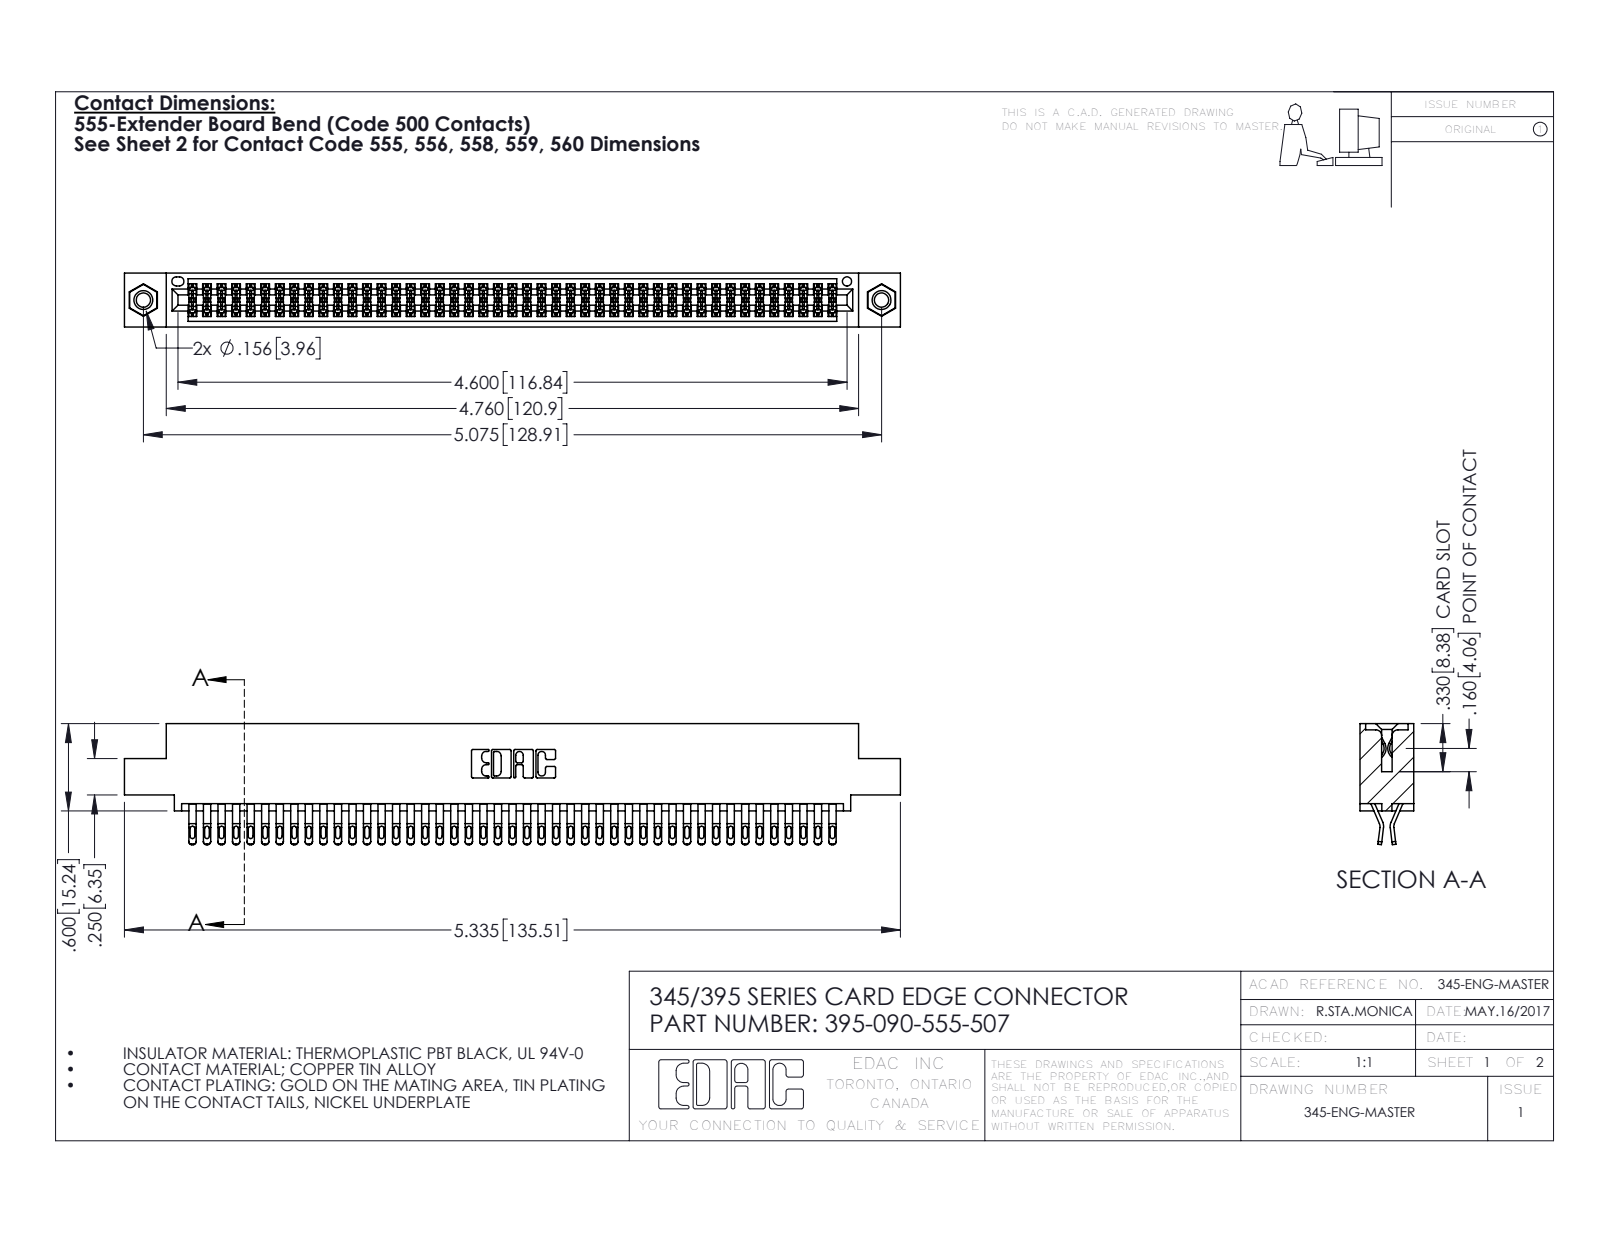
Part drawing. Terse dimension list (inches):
name: 345-292-001_555 Tail; 345 Part_0.110 Offset - 0.156 Dia-TI; 345-250-001_345-250-005-103; 395-090-555-507
written by: SolidWorks 2016 (CONFIG_CONTROL_DESIGN)
unit: in
bodies: 93 solids, 5230 faces (2906 planar, 2308 cylindrical, 16 other)
size: 5.335 × 0.832 × 0.37
volume: 0.816 in³; area: 32.31 in²
holes: 2× ⌀0.098, 2× ⌀0.125, 2× ⌀0.156, 1× ⌀0.064
bosses: 2× ⌀0.155
rounds: 225× R0.016, 180× R0.02, 135× R0.006, 22× R0.01, 6× R0.007, 6× R0.031, 3× R0.026, 2× R0.01
face distances: 0.072, 0.298, 0.025, 0.37, 0.2, 0.098, 0.272, 0.225, 0.175, 0.149
hole spacings: 0.27, 4.839, 5.075
